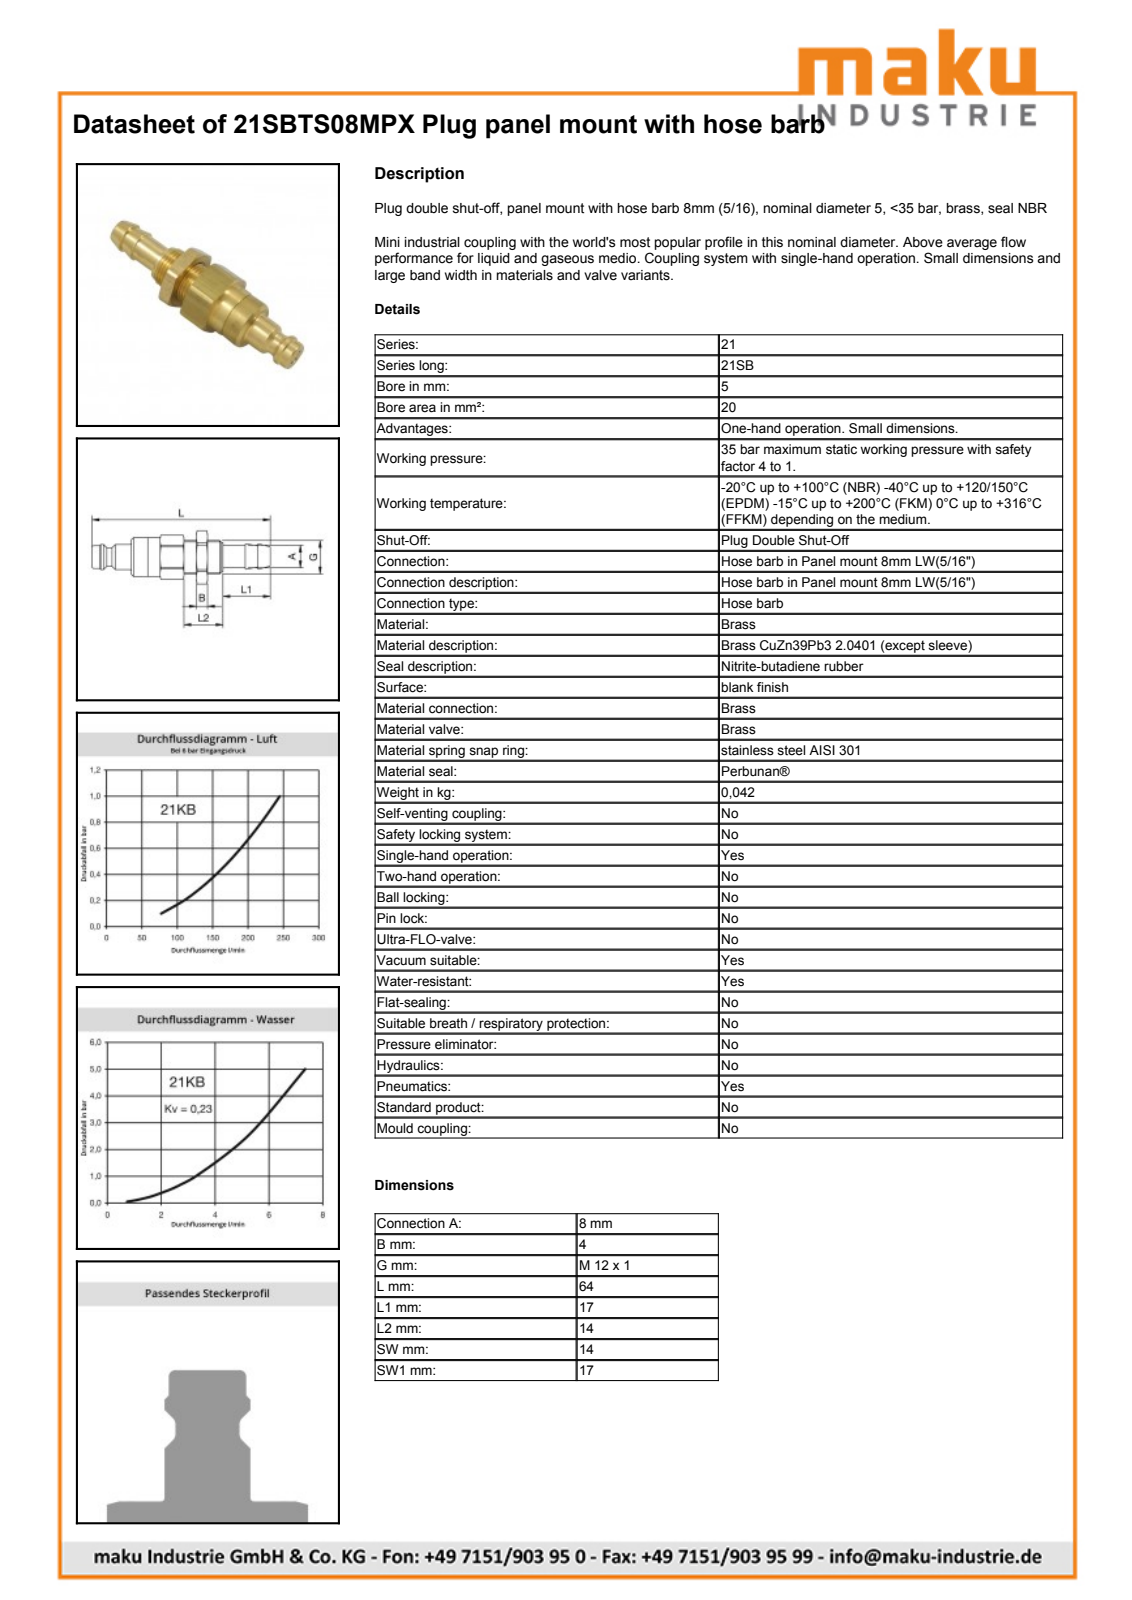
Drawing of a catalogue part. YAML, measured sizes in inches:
part_name: "D108551"
step_written_by: "Autodesk Inventor 2013 (AUTOMOTIVE_DESIGN)"
units: inches
bodies: {solids: 1, faces: 94, planar: 23, cylindrical: 25, other: 46}
overall_size: [2.52, 0.754, 0.735]
volume: 0.451
surface_area: 5.526
round_bosses_or_shafts:
  - {diameter: 0.551, count: 1}
  - {diameter: 0.472, count: 1}
  - {diameter: 0.472, count: 1}
  - {diameter: 0.433, count: 1}
  - {diameter: 0.424, count: 1}
  - {diameter: 0.417, count: 1}
  - {diameter: 0.354, count: 1}
  - {diameter: 0.319, count: 1}
partial_cylinders:
  - {radius: 0.377, count: 1}
face_to_face_distances: [0.669, 0.177, 0.335, 0.157, 0.337, 0.514, 0.671, 1.043, 0.407, 0.744]
